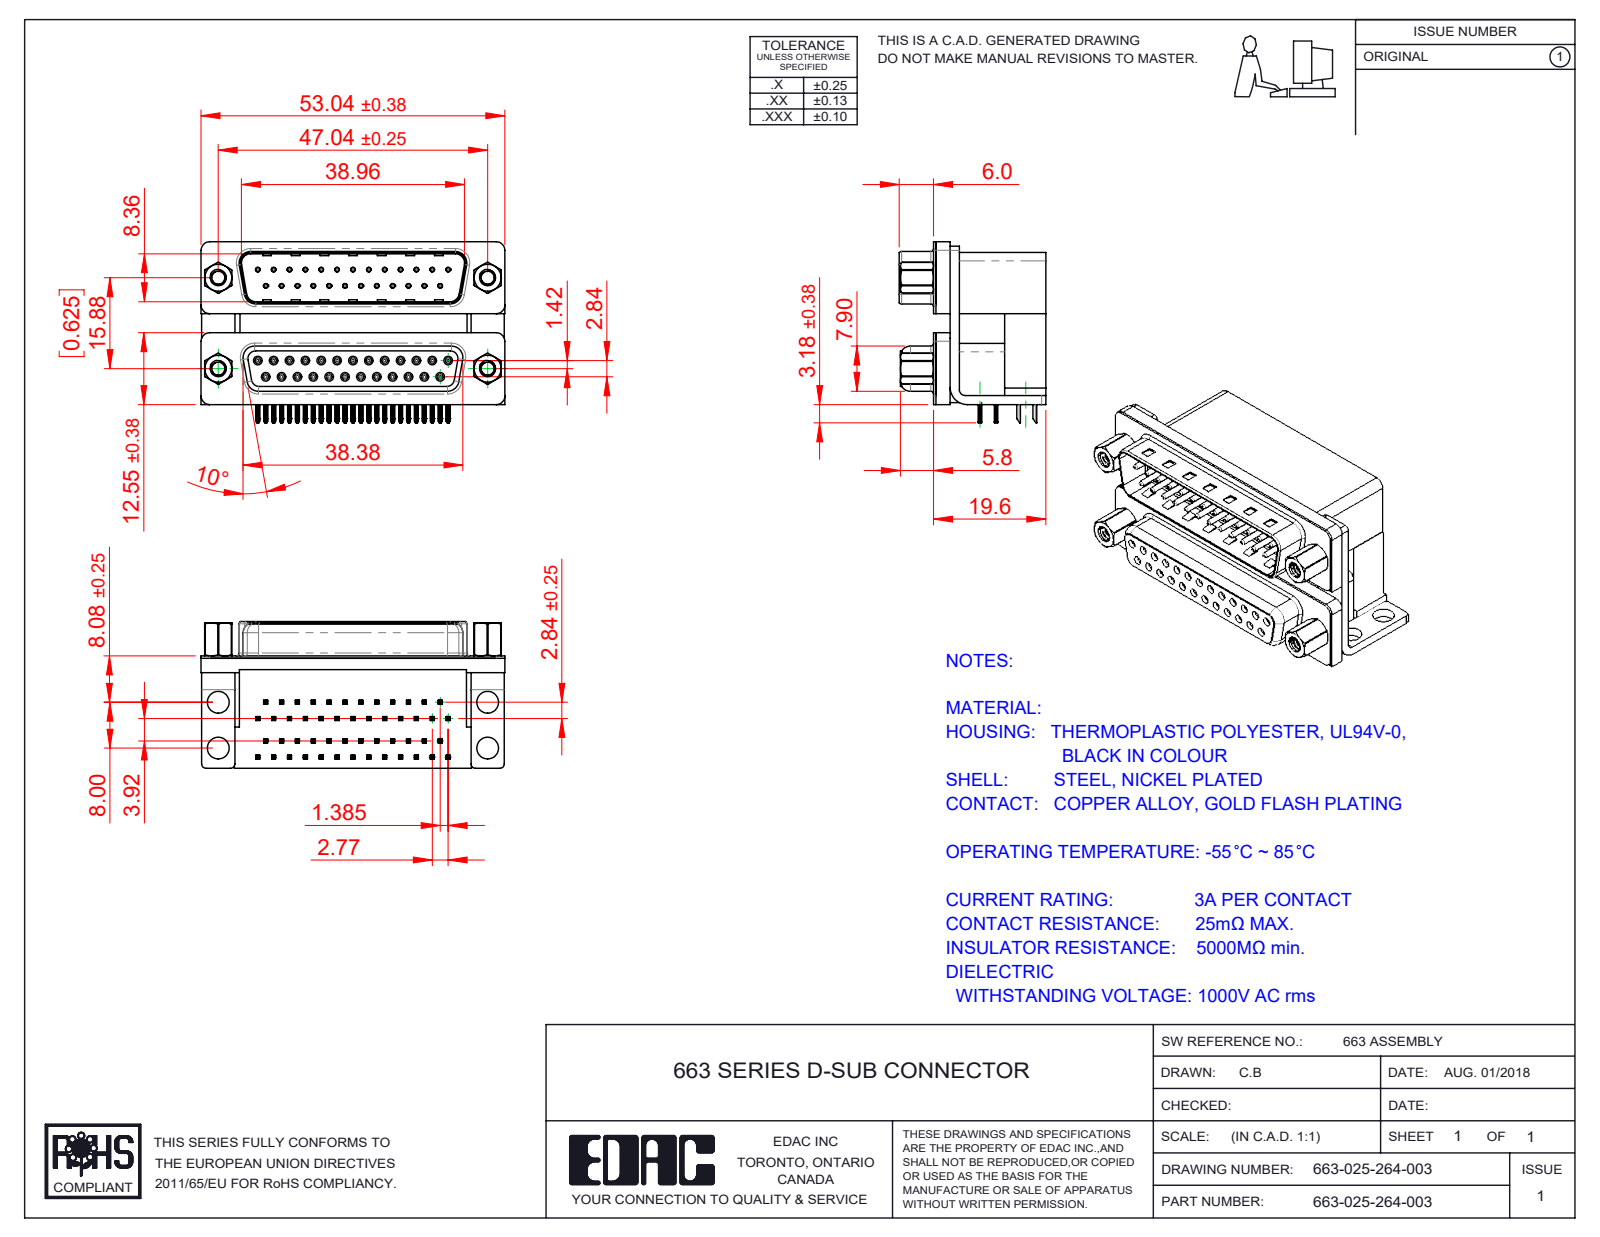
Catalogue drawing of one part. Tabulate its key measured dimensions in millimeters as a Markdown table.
| quantity | value |
| --- | --- |
| part name | 663-025-264-003; 663 4-40 Hex Standoff 5; 663 Contact Bottom Upper_L; 663 Mounting Bracket_NoneL (+8 more) |
| STEP written by | SolidWorks 2020 (CONFIG_CONTROL_DESIGN) |
| units | millimeters |
| bodies | 65 solids, 6455 faces (3301 planar, 1687 cylindrical, 1467 other) |
| overall size | 53.04 × 31.61 × 25.6 |
| volume | 22 033 mm³ |
| surface area | 23 948 mm² |
| round holes (diameter × count) | 0.8 × 50, 0.35 × 25, 0.9 × 25, 2.26 × 4, 2.29 × 4, 3.5 × 4, 3.8 × 4, 4 × 4, 4.8 × 4, 5 × 4 |
| round bosses / shafts (diameter × count) | 1.2 × 25, 0.75 × 25, 4.9 × 4, 4.75 × 4, 3.9 × 4, 2.79 × 4 |
| partial cylindrical surfaces (radius × count) | 0.1 × 200, 0.15 × 100, 0.25 × 100, 0.12 × 50, 0.35 × 50, 0.34 × 25, 1.5 × 13, 0.28 × 12 |
| main face-to-face distances | 0.4, 19.2, 7.2, 12, 10.7, 16.7, 9.5, 2.5, 15.53, 2.9 |
| hole center spacings | 3.16, 2.77, 5.54, 11.08, 8.31, 5.03, 13.85, 7.48 |
